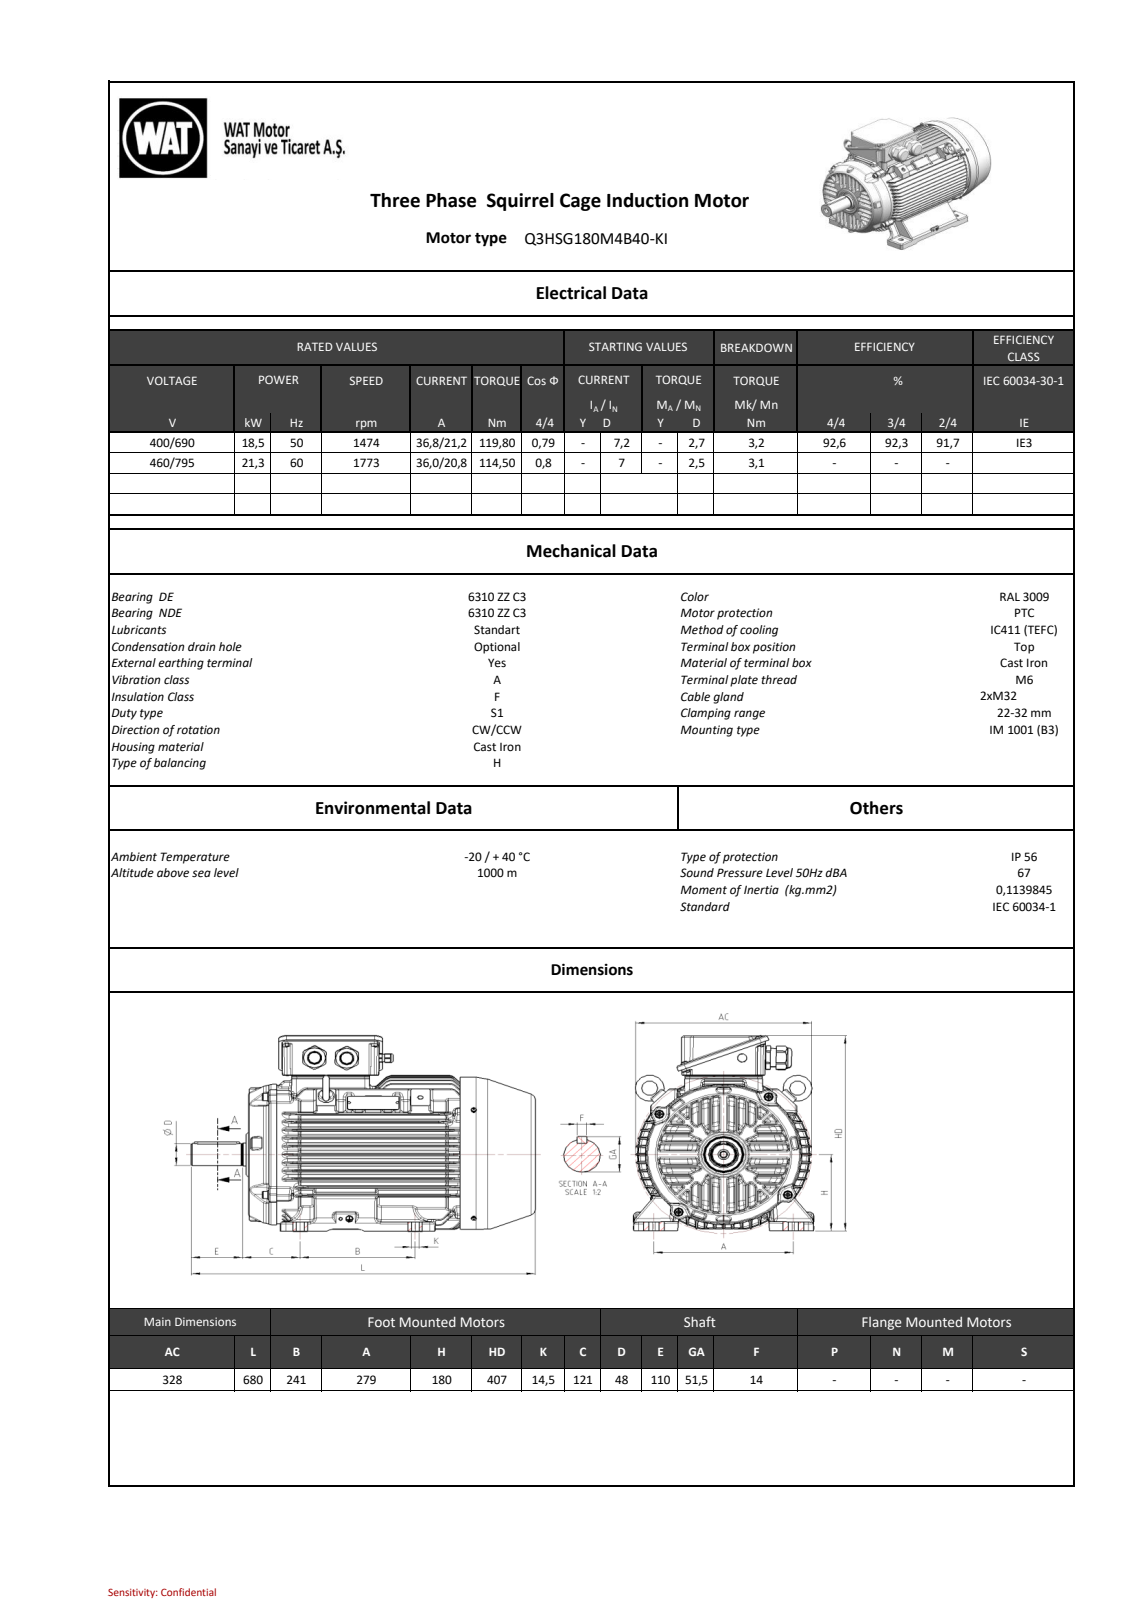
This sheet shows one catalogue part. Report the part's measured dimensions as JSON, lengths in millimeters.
{"part_name": "C90176C46D272aui", "step_written_by": "SIEMENS PLM Software NX 11.0 (AUTOMOTIVE_DESIGN)", "units": "millimeters", "bodies": {"solids": 0, "faces": 6817, "planar": 1251, "cylindrical": 1823, "other": 3743}, "overall_size": [680, 408.31, 346], "round_holes": [[8.5, 8], [2.5, 2], [10.3, 2], [5, 1], [6.3, 1], [10, 1], [14, 1], [17, 1], [19, 1], [21, 1], [75.8, 1], [194, 1]], "round_bosses_or_shafts": [[16, 8], [20, 4], [10, 4], [8, 4], [5, 4], [25, 2], [8.65, 2], [317, 1]], "partial_cylinders_radius": [[5, 280], [3, 177], [4, 120], [1.5, 112], [2, 63], [1.8, 60], [0.4, 31], [1, 30]], "face_to_face_distances": [15.17, 137.45, 15.25, 122.2, 30.42, 45.73, 106.89, 30.56, 15.31, 61.11], "hole_center_spacings": [144, 203.65, 50.01, 165.2, 235.92, 283.63, 288.01, 47.5]}
